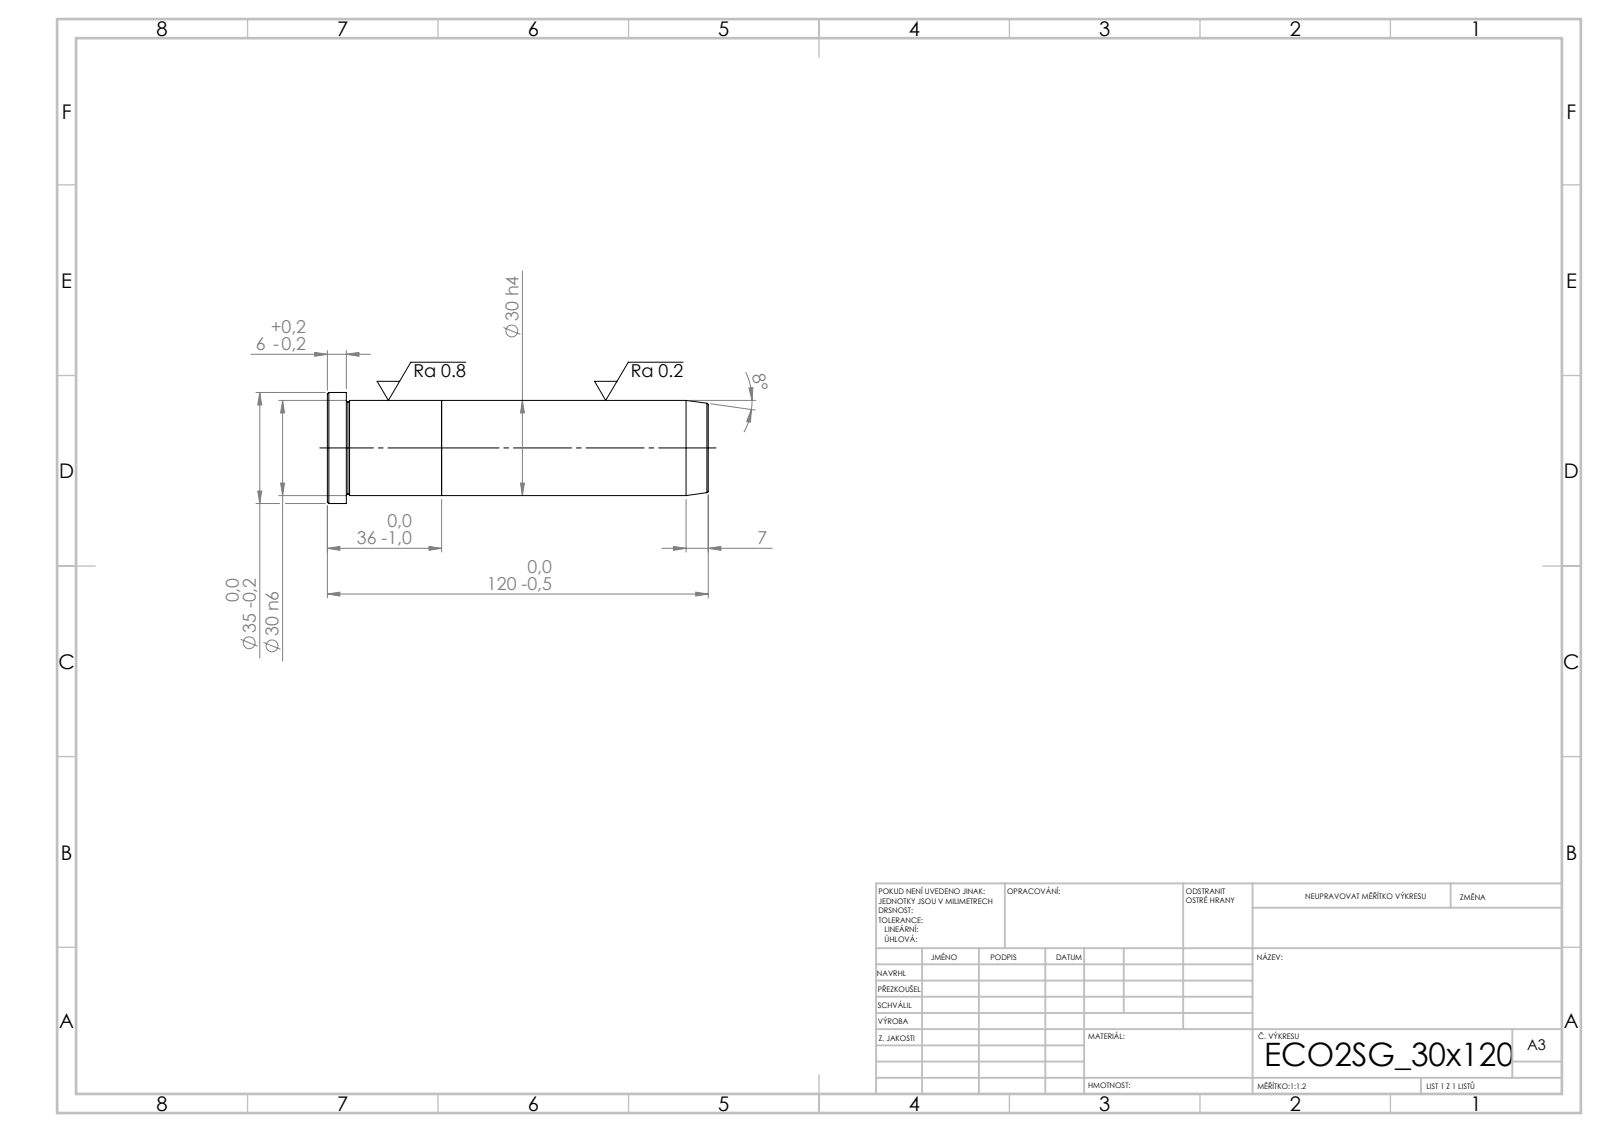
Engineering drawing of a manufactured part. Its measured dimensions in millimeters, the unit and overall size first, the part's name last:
Units: millimetres
Overall size (bounding box): 120 × 35 × 35
Round bosses / shafts (diameter × count): ⌀35 ×1, ⌀30 ×1
Main face-to-face distances: 36, 84, 120, 114, 30, 6
Volume: 85 984 mm³ · Surface area: 14 641 mm²
Bodies: 2 solids, 21 faces (5 planar, 6 cylindrical, 10 other)
STEP written by: SolidWorks 2019 (CONFIG_CONTROL_DESIGN)
